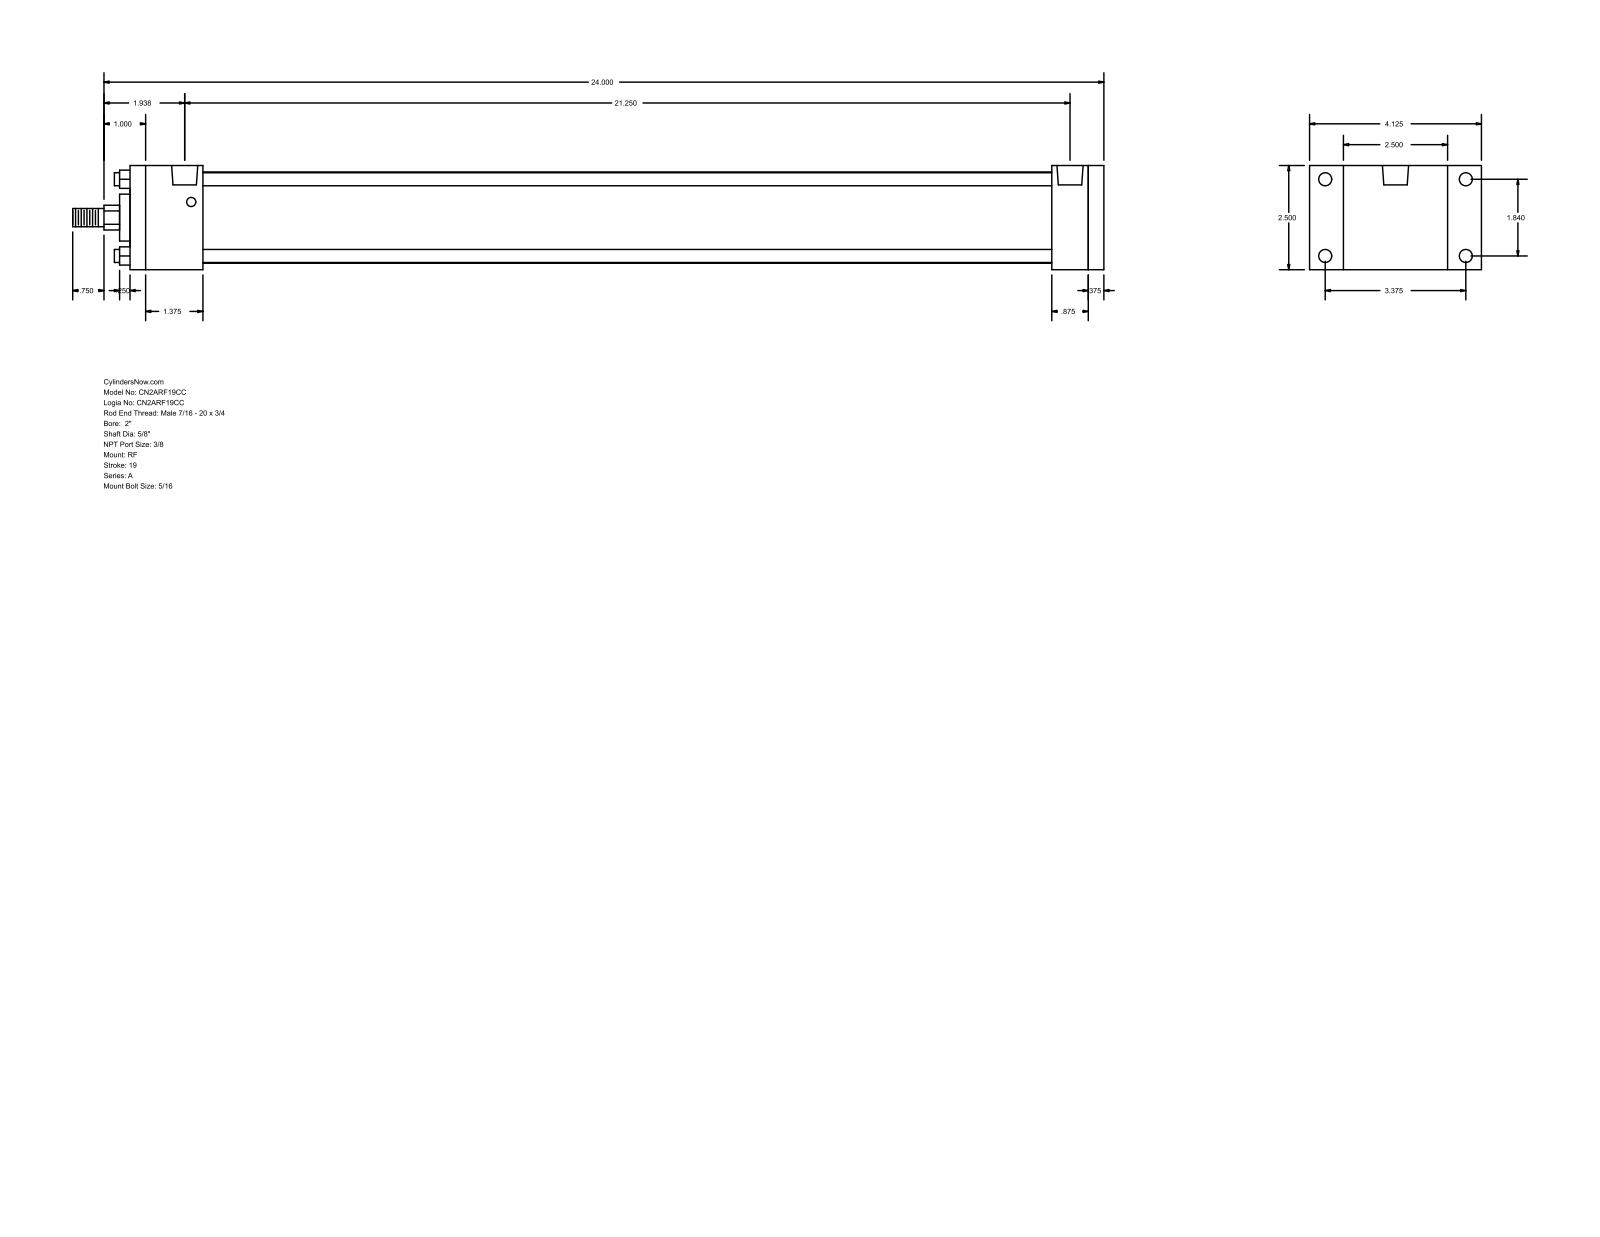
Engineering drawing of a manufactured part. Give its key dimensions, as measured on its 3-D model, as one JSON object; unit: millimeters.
{"part_name": "A_RF__0200_0.625", "step_written_by": "GSSL Pune (CONFIG_CONTROL_DESIGN)", "units": "millimeters", "bodies": {"solids": 0, "faces": 92, "planar": 64, "cylindrical": 28, "other": 0}, "overall_size": [628.65, 104.78, 63.5], "round_holes": [[5.56, 4], [7.94, 4], [15.93, 2]], "round_bosses_or_shafts": [[7.94, 4], [55.63, 1], [28.57, 1], [15.88, 1], [11.11, 1]], "partial_cylinders_radius": [[7.54, 1]], "face_to_face_distances": [63.5, 593.72, 584.2, 9.52, 44.45, 539.75, 549.27, 561.97, 517.52, 22.23], "hole_center_spacings": [46.74, 85.72, 97.63, 531.8, 3.97, 3.98, 535.77, 535.78]}
